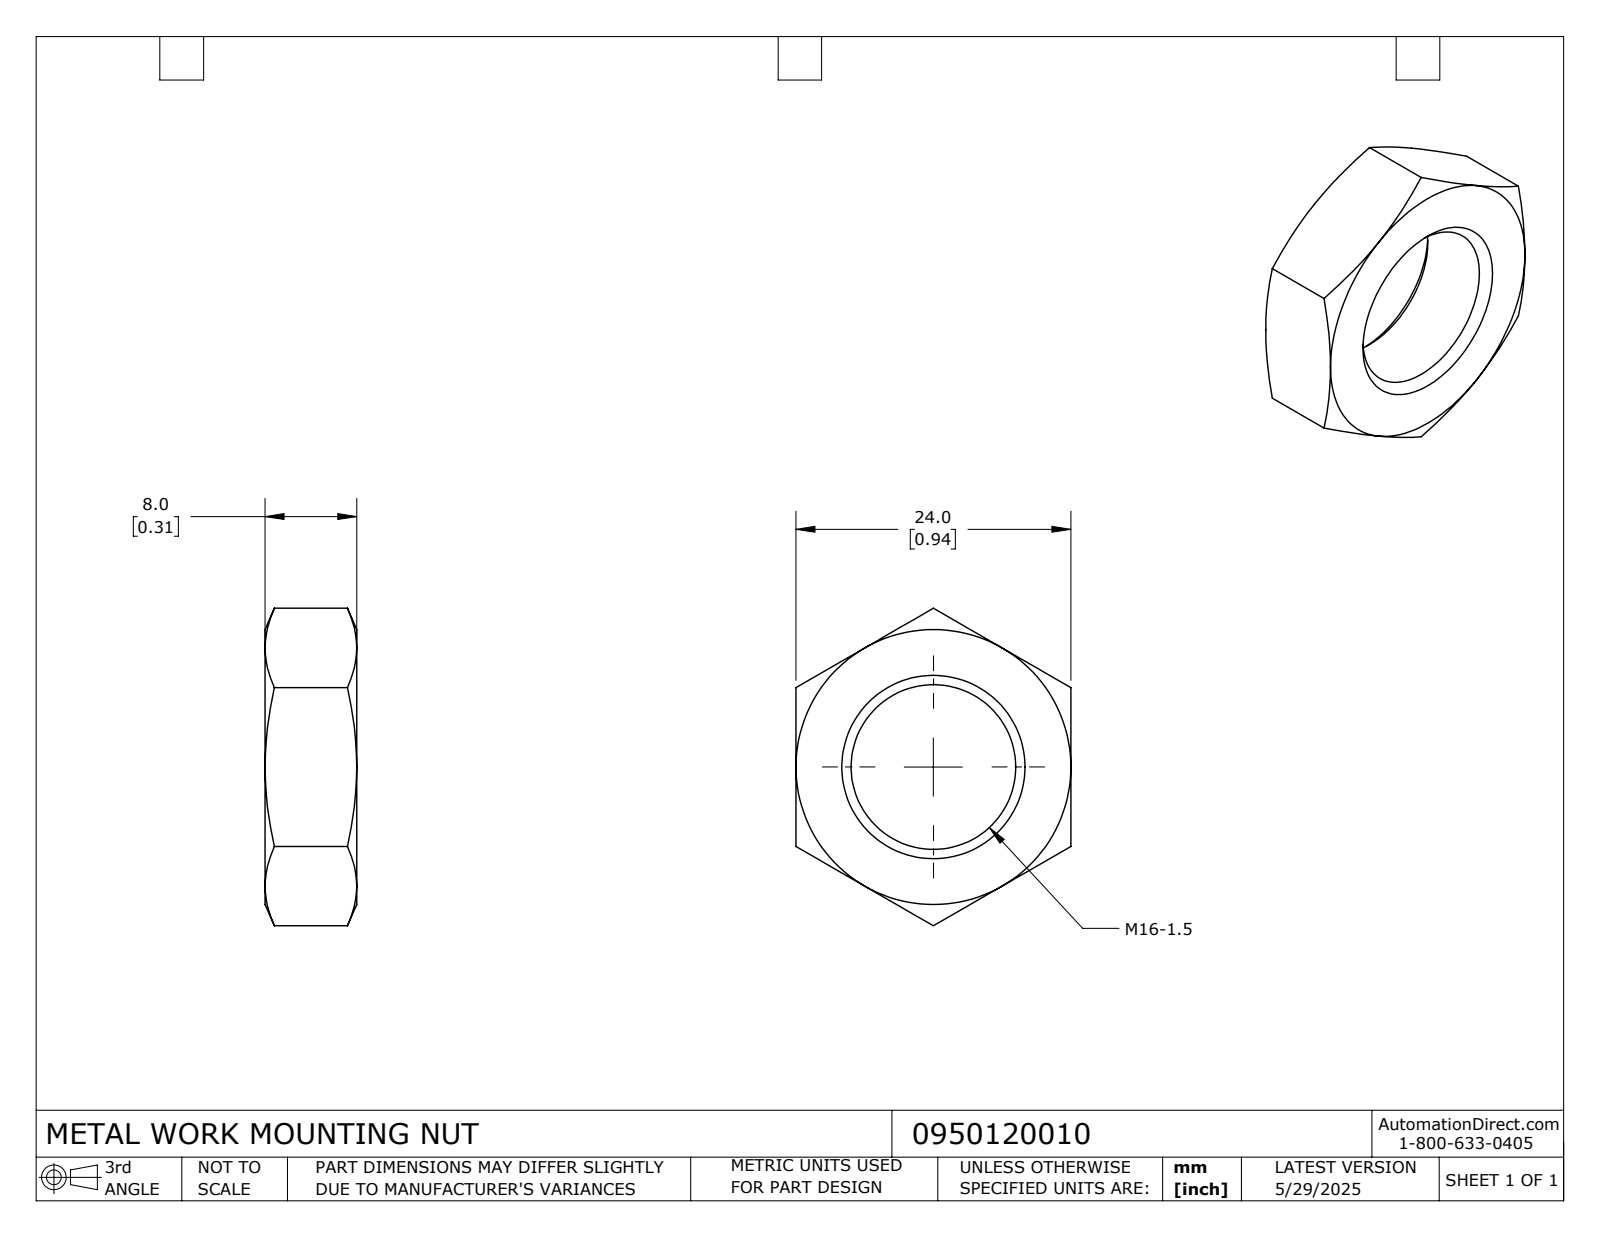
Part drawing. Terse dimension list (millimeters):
name: 0950120010
written by: SolidWorks 2024 (CONFIG_CONTROL_DESIGN)
unit: mm
bodies: 1 solid, 26 faces (8 planar, 2 cylindrical, 16 other)
size: 27.71 × 24 × 8
volume: 2 639 mm³; area: 1 621 mm²
holes: 1× ⌀14.38
face distances: 24, 8
